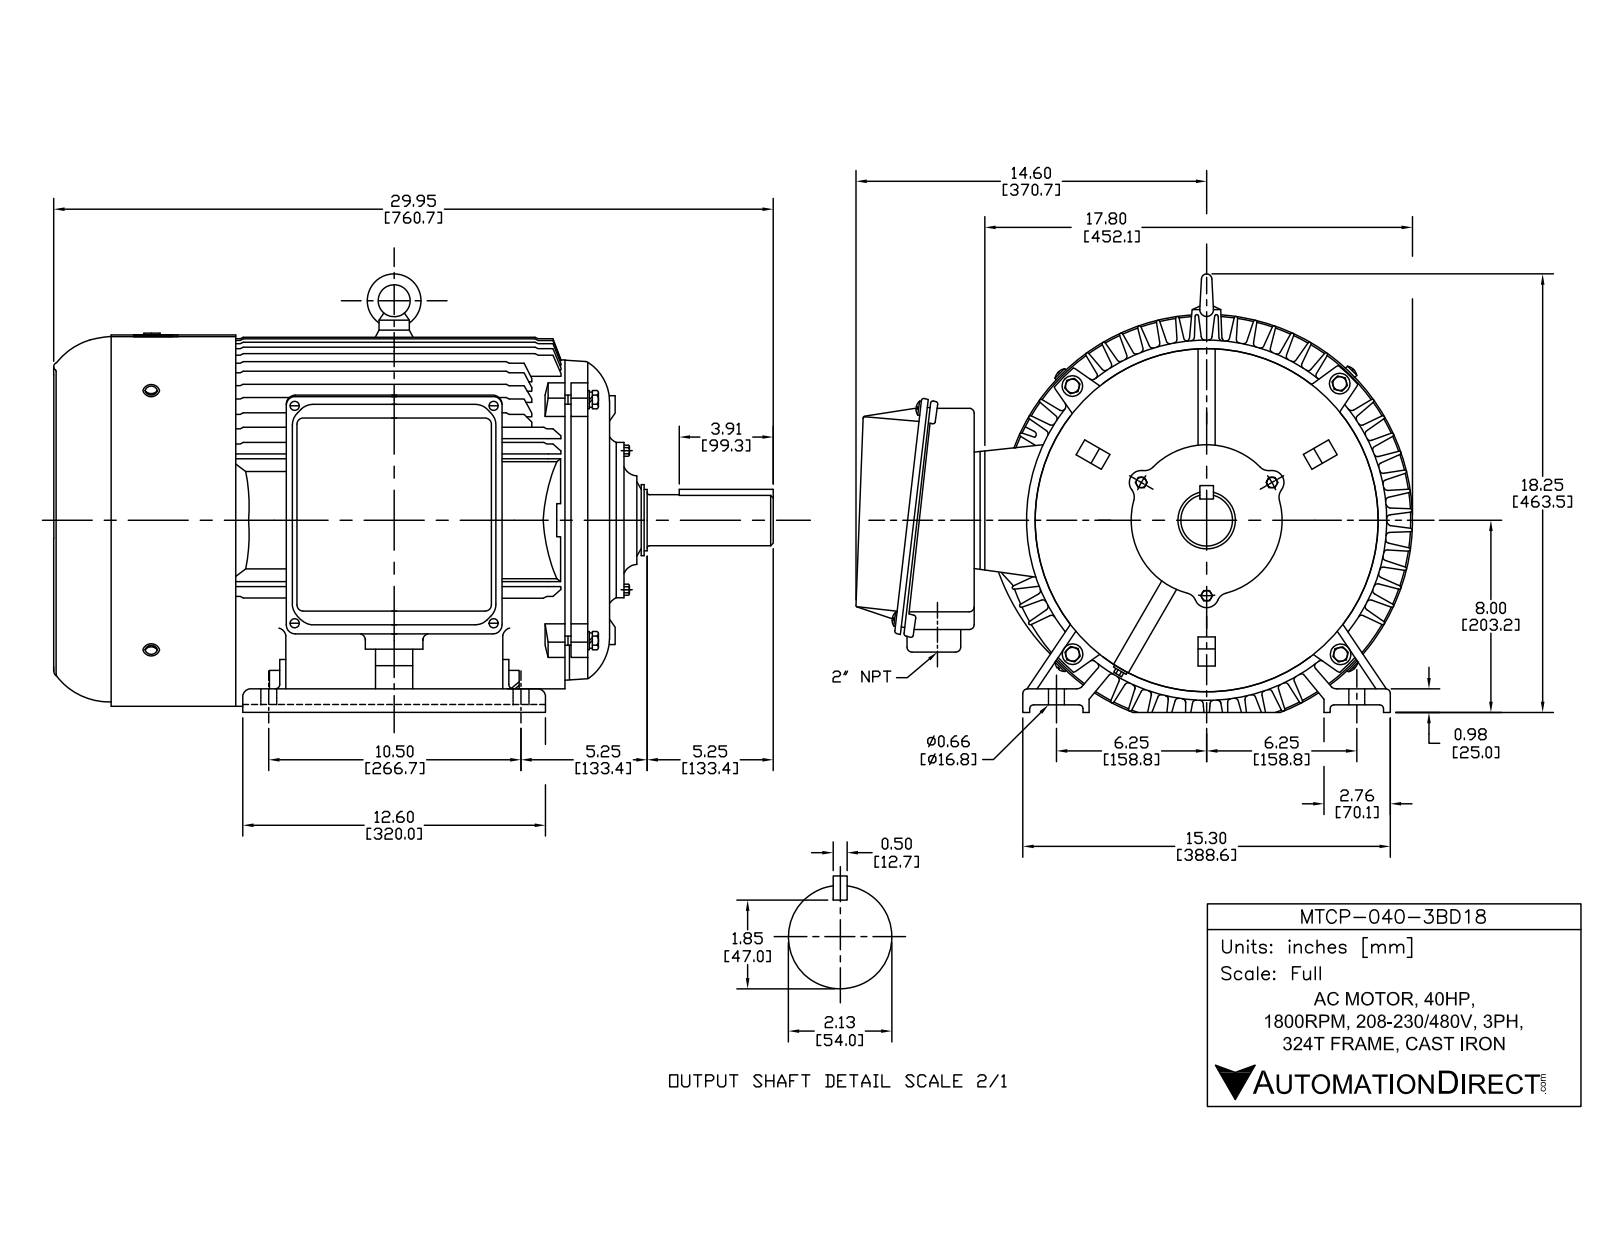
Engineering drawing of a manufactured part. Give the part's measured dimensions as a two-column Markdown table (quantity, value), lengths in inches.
| quantity | value |
| --- | --- |
| part name | 17橡皮塞; plain washers-chamfered--normal series-a gb_GB_FASTENER_WASHER_SWCA 6; hex head bolts-full thread grade c gb_GB_FASTENER_BOLT_HHBFTC M8X55-N; hex head bolts-full thread grade c gb_GB_FASTENER_BOLT_HHBFTC M12X55-N (+8 more) |
| STEP written by | SolidWorks 2017 (AUTOMOTIVE_DESIGN) |
| units | inches |
| bodies | 68 solids, 4082 faces (1157 planar, 1473 cylindrical, 1452 other) |
| overall size | 29.232 × 23.004 × 20.37 |
| volume | 937.3 in³ |
| surface area | 5 923 in² |
| round holes (diameter × count) | 0.394 × 21, 0.268 × 8, 0.081 × 4, 0.197 × 4, 0.252 × 4, 0.263 × 4, 0.335 × 4, 0.354 × 4, 0.402 × 4, 0.448 × 4, 0.508 × 4, 0.512 × 4 |
| round bosses / shafts (diameter × count) | 0.315 × 11, 0.472 × 8, 0.945 × 4, 0.752 × 4, 0.389 × 4, 0.236 × 4, 0.394 × 2, 17.52 × 1 |
| partial cylindrical surfaces (radius × count) | 0.039 × 213, 0.197 × 104, 0.118 × 80, 0.02 × 48, 0.394 × 37, 0.059 × 35, 0.03 × 24, 0.138 × 20 |
| main face-to-face distances | 0.236, 0.059, 4.878, 22.224, 22.165, 0.079, 0.276, 0.335, 22.559, 22.5 |
| hole center spacings | 3.937, 8.189, 2.953, 5.352, 5.501, 5.568, 5.704, 6.411 |
